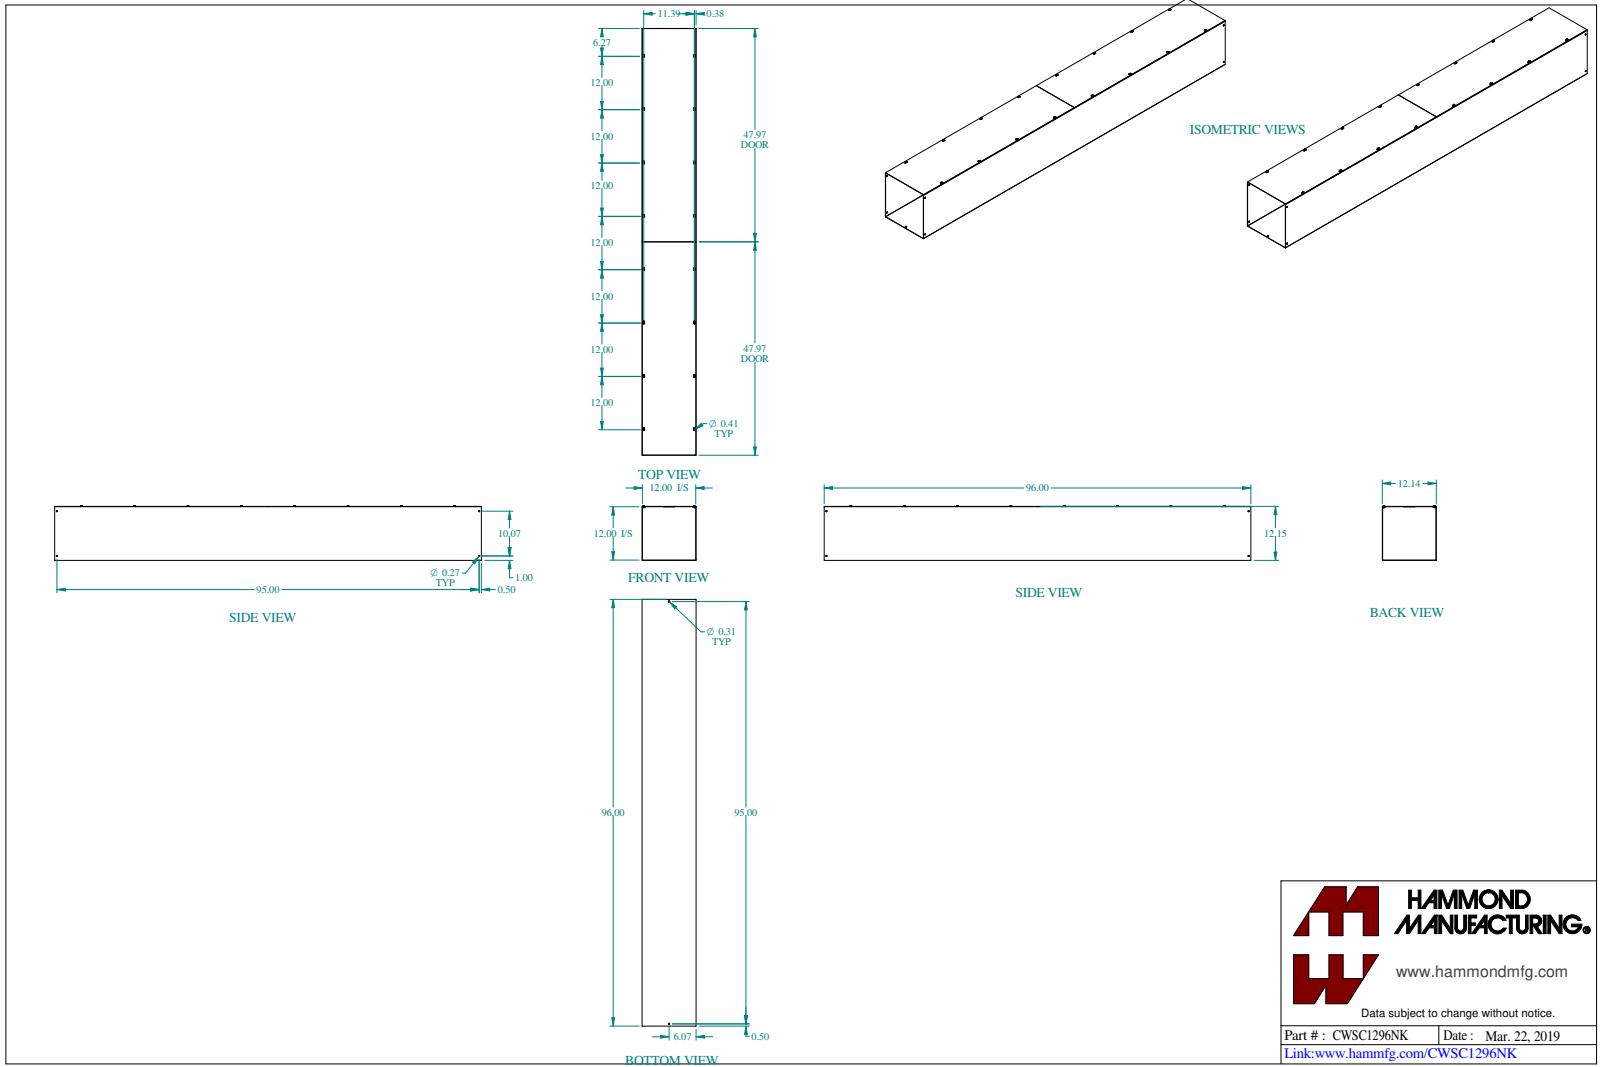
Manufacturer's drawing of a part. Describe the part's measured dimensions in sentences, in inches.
The part is named "CWSC1296NK". Its 3-D file was written by "SolidWorks 2023 (CONFIG_CONTROL_DESIGN)". It is 19 solids with 558 faces: 274 planar, 188 cylindrical and 96 other. Overall it measures 96 by 12.325 by 12.144 inches. Its volume is 348.6 cubic inches and its surface area 9 532 square inches. Round holes: 16 of diameter 0.177, 4 of diameter 0.266, 2 of diameter 0.313. Round bosses or shafts: 16 of diameter 0.375, 16 of diameter 0.19. Partial cylindrical surfaces (rounded edges, fillets, slot ends): 16 of radius 0.125, 16 of radius 0.203, 4 of radius 0.036, 4 of radius 0.108. The main face-to-face distances are 0.072, 12.072, 12, 0.078, 12.15, 12.078, 12.144, 11.928, 0.15, 0.031. The hole center spacings are 12, 16.547, 24, 26.567, 36, 37.76, 11.394, 48.
